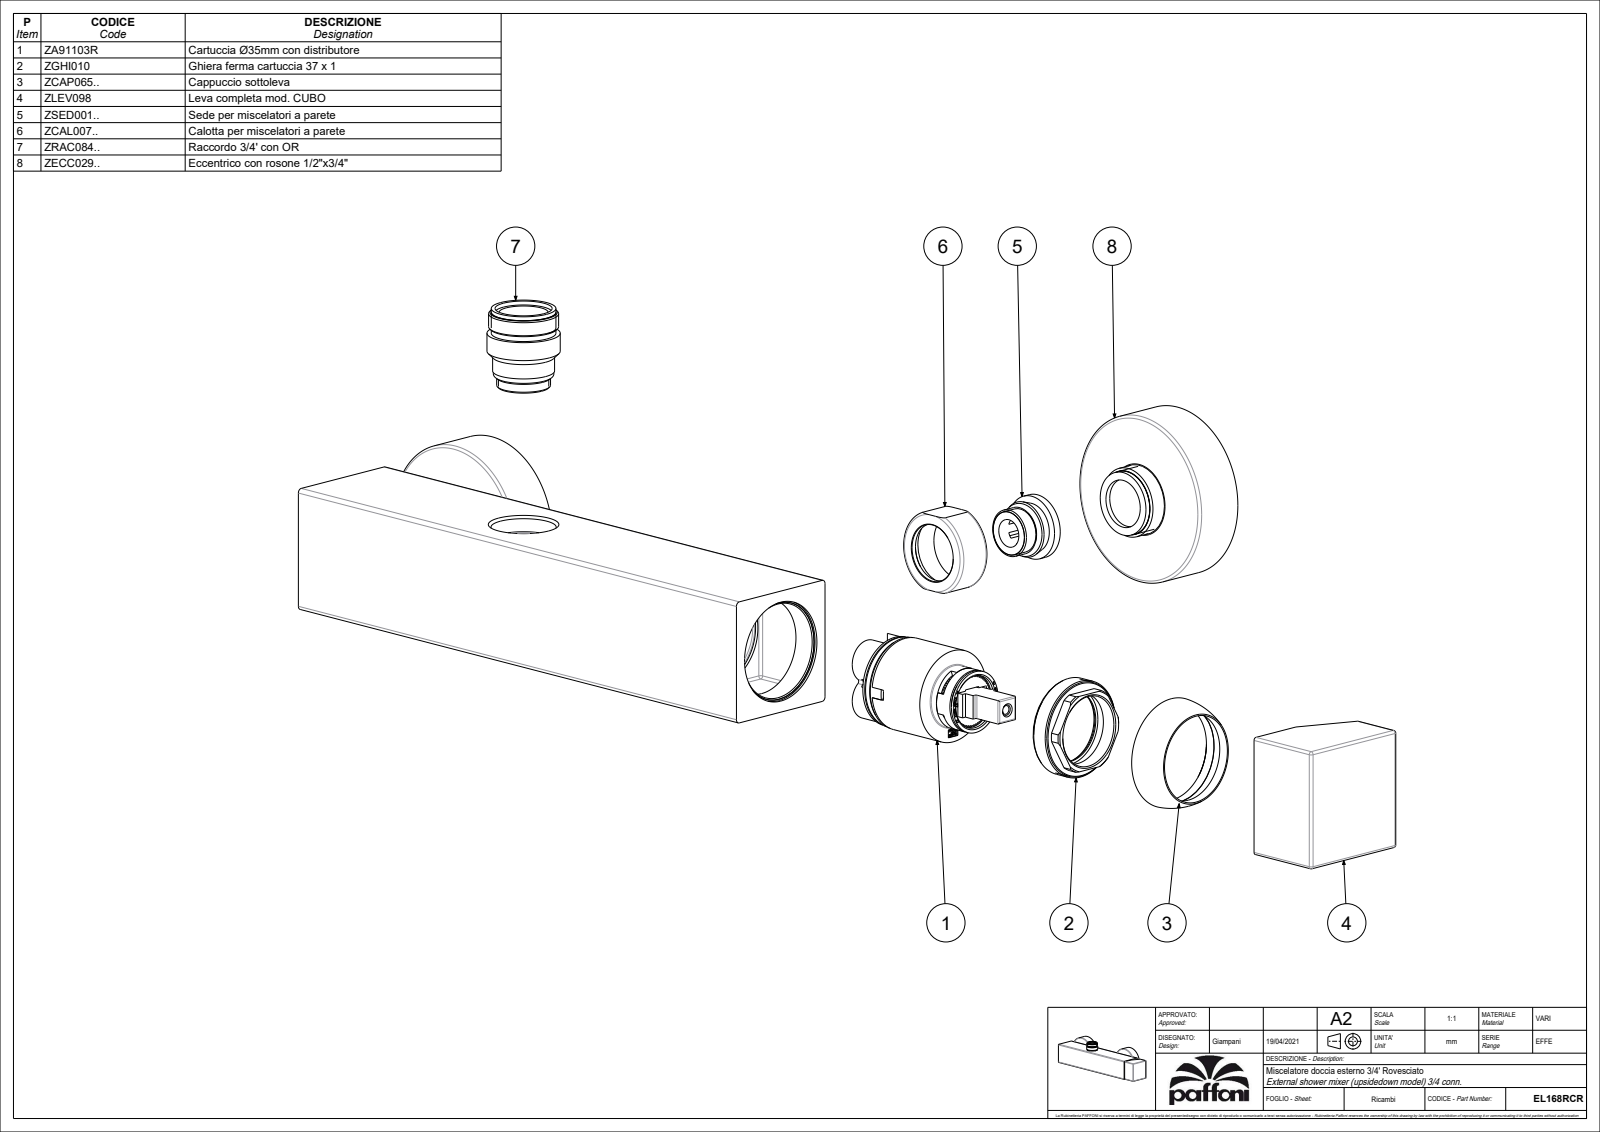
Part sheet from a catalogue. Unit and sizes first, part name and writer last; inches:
Units: inches
Overall size (bounding box): 10.738 × 3.209 × 2.874
Round holes (diameter × count): ⌀1.654 ×1
Round bosses / shafts (diameter × count): ⌀2.5 ×2, ⌀1.071 ×1, ⌀1.024 ×1, ⌀0.945 ×1, ⌀0.709 ×1, ⌀0.591 ×1, ⌀0.354 ×1, ⌀0.315 ×1
Partial cylindrical surfaces — rounded edges, fillets, slot ends (radius × count): R0.039 ×8, R0.059 ×4, R0.614 ×2, R0.118 ×1, R0.156 ×1
Main face-to-face distances: 1.831, 1.378, 3.209, 0.591, 0.787, 2.421, 0.03, 1.801, 1.772, 10.276
Volume: 42.24 in³ · Surface area: 130 in²
Bodies: 1 solid, 117 faces (36 planar, 44 cylindrical, 37 other)
Part name (STEP PRODUCT): EL168RCR
STEP written by: CREO PARAMETRIC BY PTC INC, 2020044 (CONFIG_CONTROL_DESIGN)
